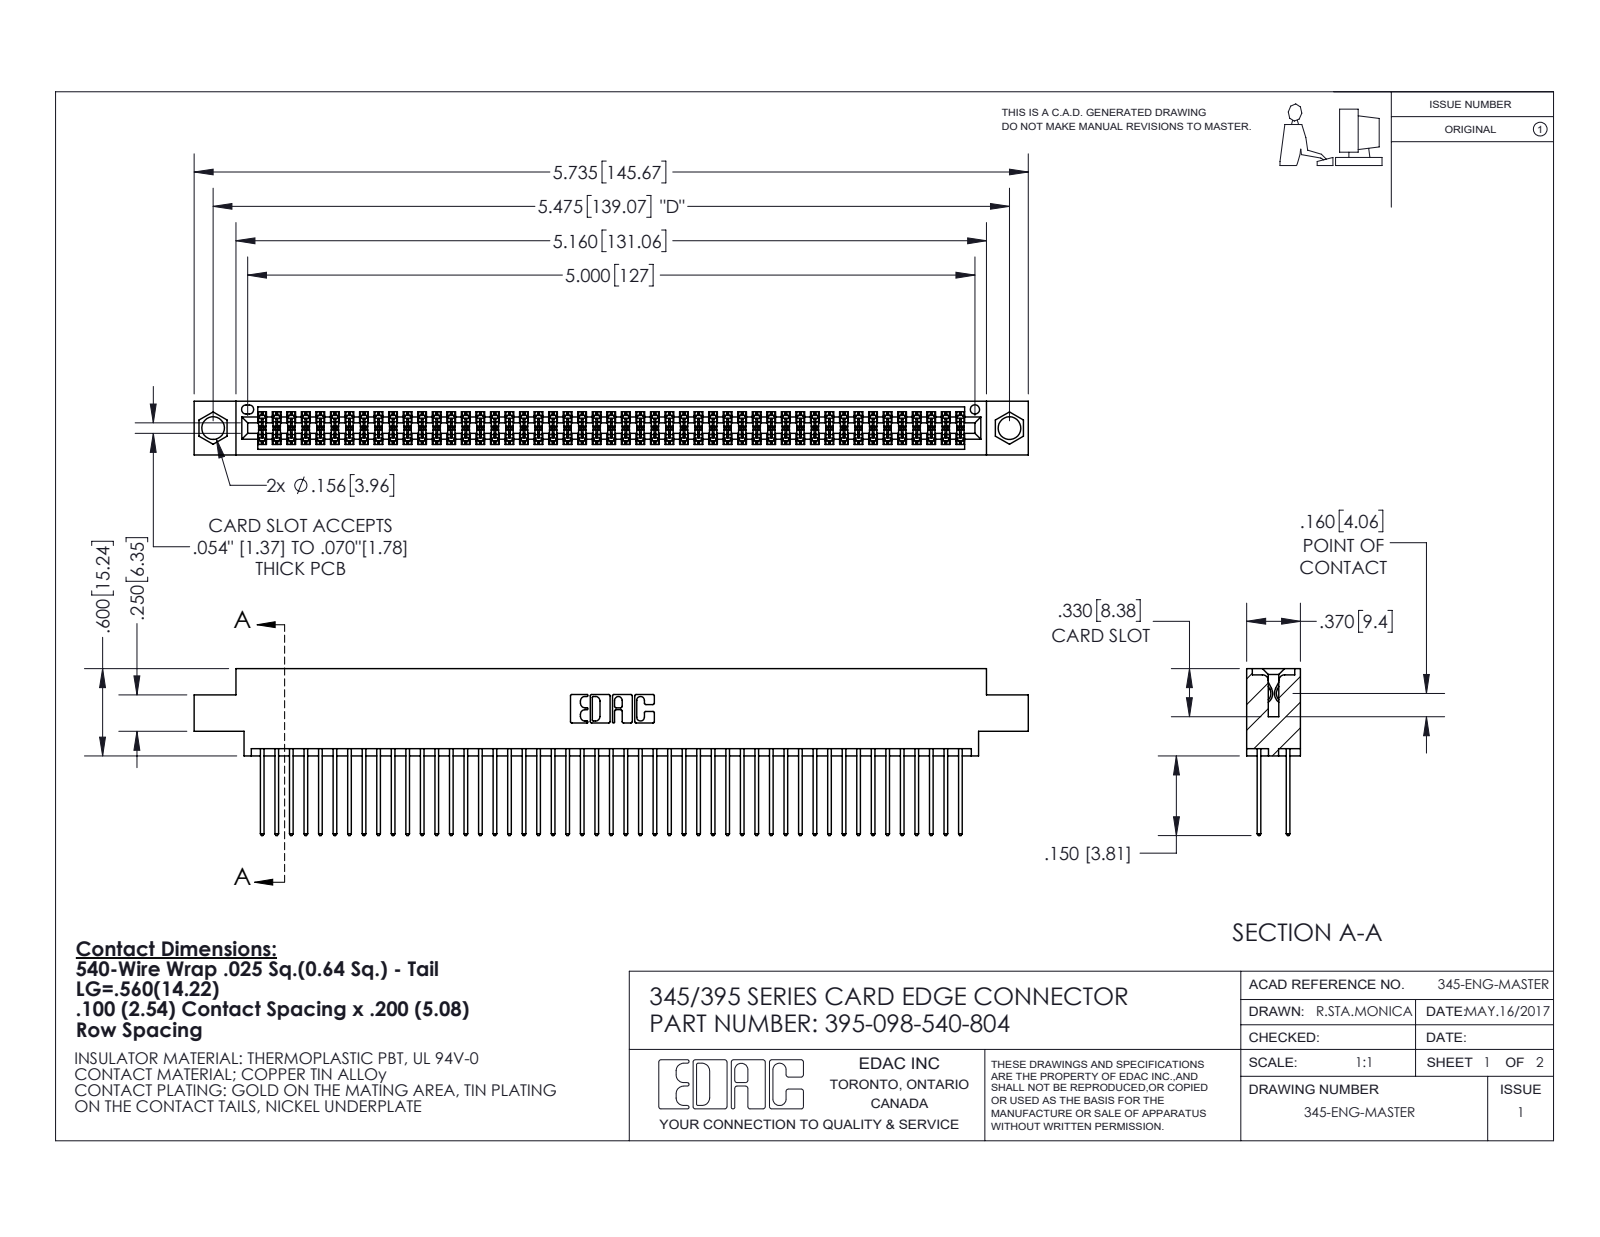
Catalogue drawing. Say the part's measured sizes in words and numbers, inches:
The part is named "345 Part_0.170 Offset - 0.156 Dia-TI; 395-098-540-804; 345-292-001_345-293-140". Its 3-D file was written by "SolidWorks 2020 (CONFIG_CONTROL_DESIGN)". It is 99 solids with 5044 faces: 3332 planar, 1712 cylindrical and 0 other. Overall it measures 5.735 by 1.147 by 0.37 inches. Its volume is 0.877 cubic inches and its surface area 35.79 square inches. Round holes: 2 of diameter 0.156, 1 of diameter 0.064. Partial cylindrical surfaces (rounded edges, fillets, slot ends): 196 of radius 0.006, 98 of radius 0.01, 22 of radius 0.01, 6 of radius 0.007, 6 of radius 0.031, 3 of radius 0.026, 2 of radius 0.014, 2 of radius 0.019. The main face-to-face distances are 0.072, 0.298, 0.2, 0.098, 0.272, 0.025, 0.37, 0.225, 0.175, 0.149. The hole center spacings are 0.27, 5.239, 5.475.
